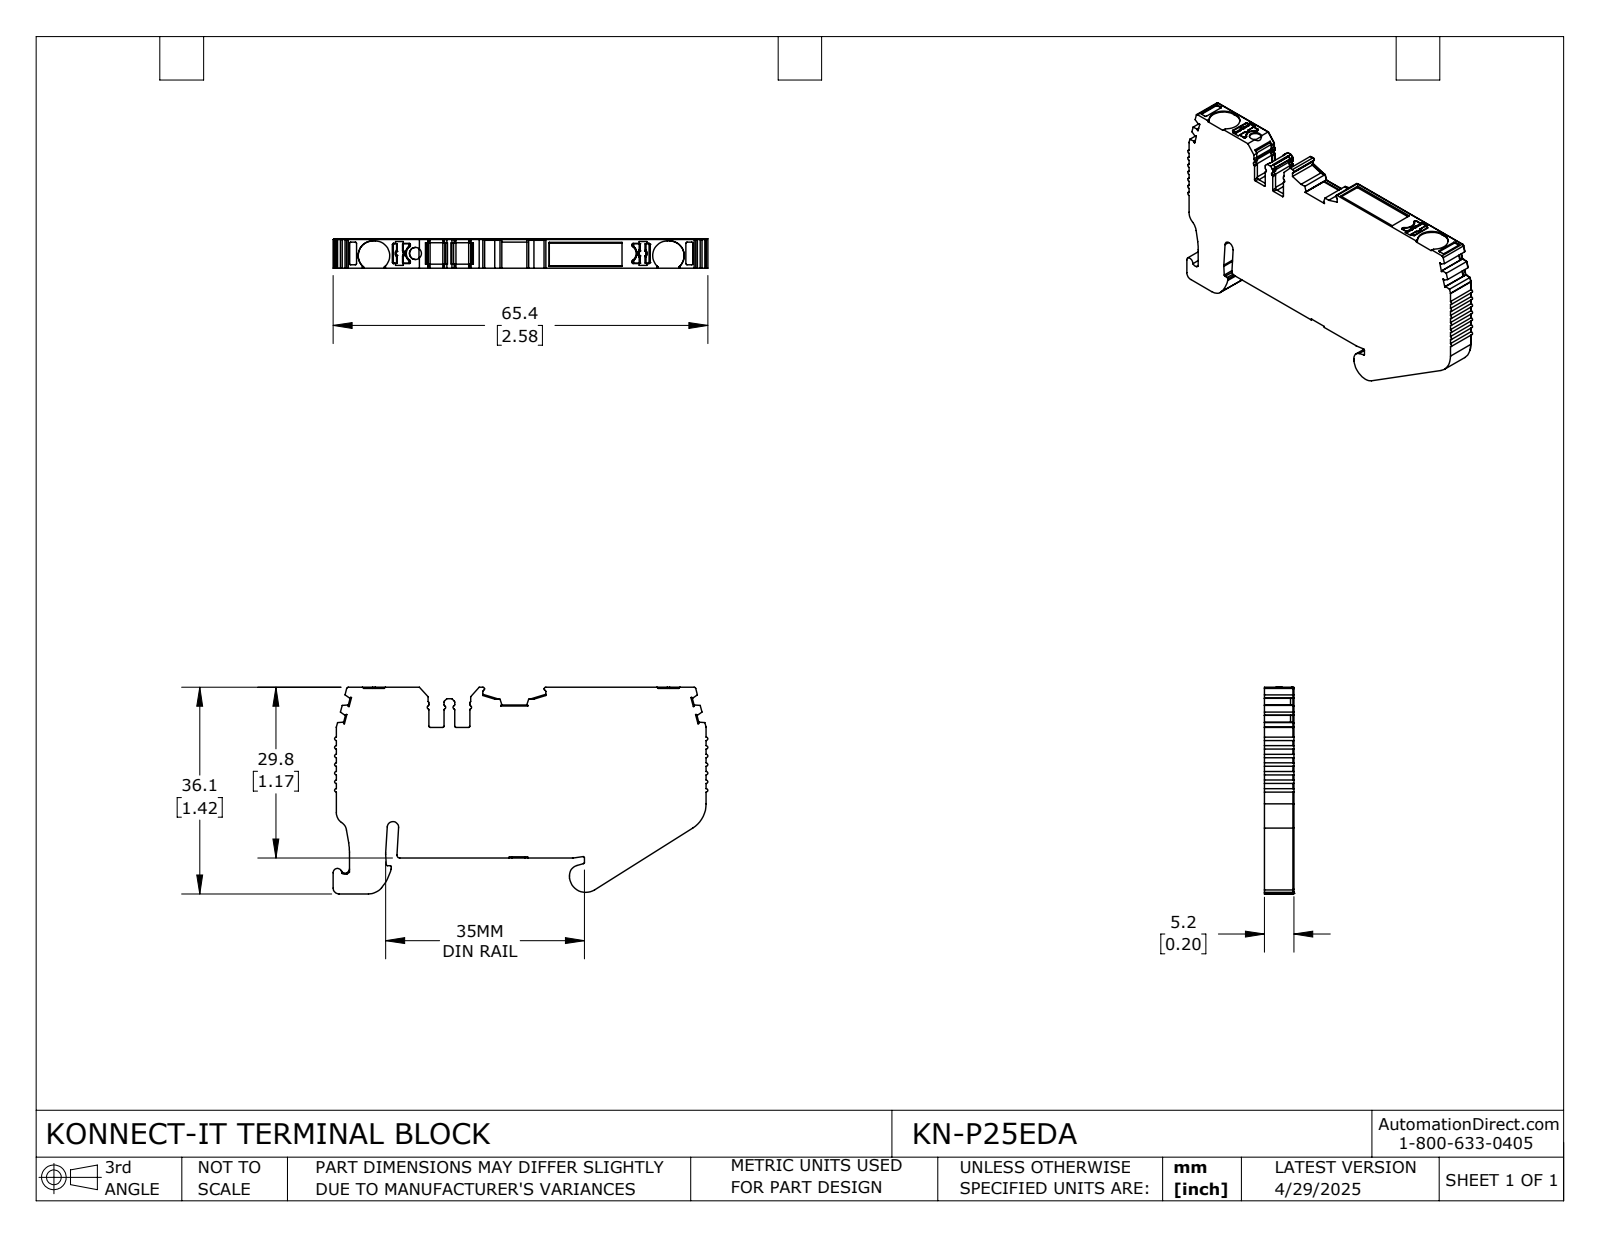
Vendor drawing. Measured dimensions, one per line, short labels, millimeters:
name: KN-P25EDA
written by: SolidWorks 2024 (CONFIG_CONTROL_DESIGN)
unit: mm
bodies: 1 solid, 594 faces (327 planar, 230 cylindrical, 37 other)
size: 65.4 × 36.1 × 5.2
volume: 9 570 mm³; area: 5 135 mm²
holes: 1× ⌀2.1
rounds: 54× R0.2, 39× R0.3, 18× R0.5, 17× R0.1, 9× R0.4, 8× R0.2, 4× R2.5, 3× R1
face distances: 5.2, 29.6, 29.8, 64.6, 4.5, 5, 6.2, 35.9, 2, 36.1
